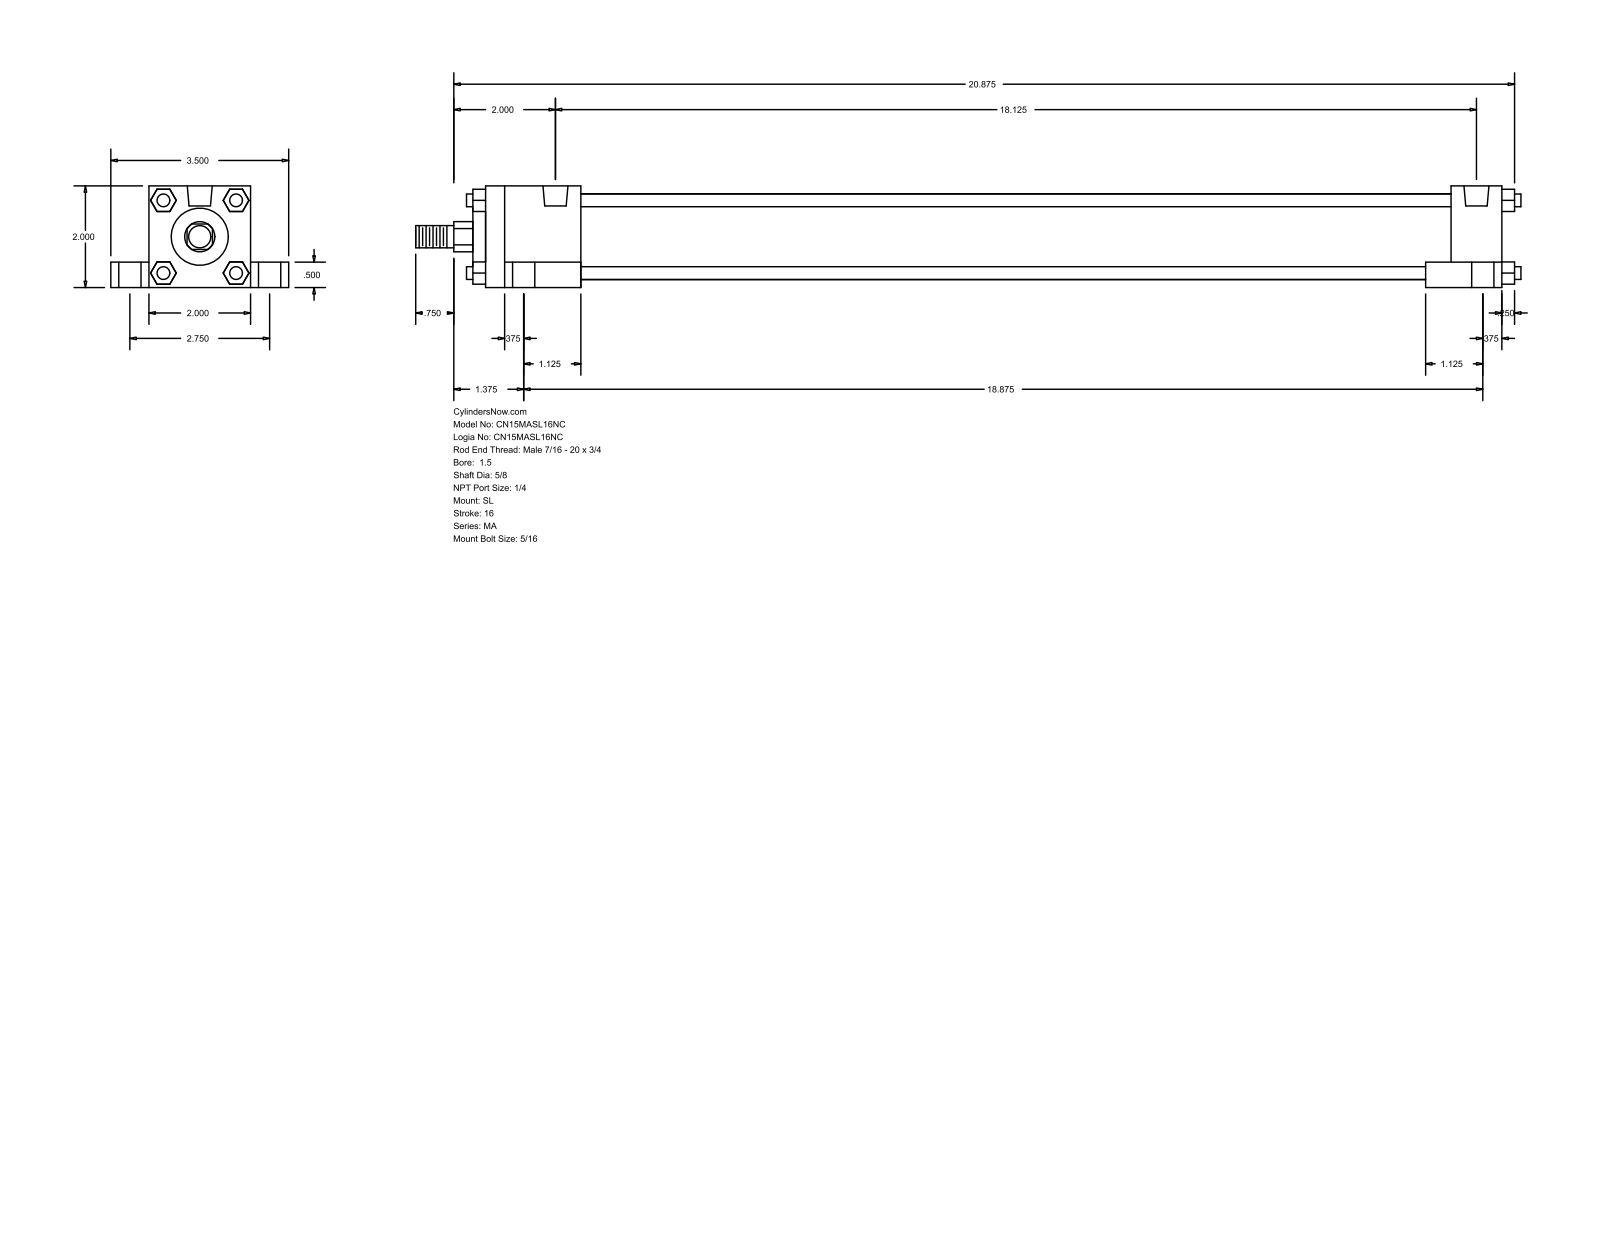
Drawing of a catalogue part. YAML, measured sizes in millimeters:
part_name: "MA_SL__0150_0.625"
step_written_by: "GSSL Pune (CONFIG_CONTROL_DESIGN)"
units: millimeters
bodies: {solids: 0, faces: 148, planar: 112, cylindrical: 36, other: 0}
overall_size: [552.45, 88.9, 50.8]
round_holes:
  - {diameter: 7.94, count: 4}
  - {diameter: 11.11, count: 4}
  - {diameter: 17.46, count: 4}
  - {diameter: 12.49, count: 2}
round_bosses_or_shafts:
  - {diameter: 6.35, count: 4}
  - {diameter: 42.93, count: 1}
  - {diameter: 28.57, count: 1}
  - {diameter: 15.88, count: 1}
  - {diameter: 11.11, count: 1}
partial_cylinders:
  - {radius: 7.54, count: 1}
face_to_face_distances: [50.8, 19.05, 38.1, 508, 69.85, 12.7, 9.52, 25.4, 6.35, 514.35]
hole_center_spacings: [35.06, 38.36, 69.84, 460.38, 464.86, 477.54, 479.43, 484.49]
